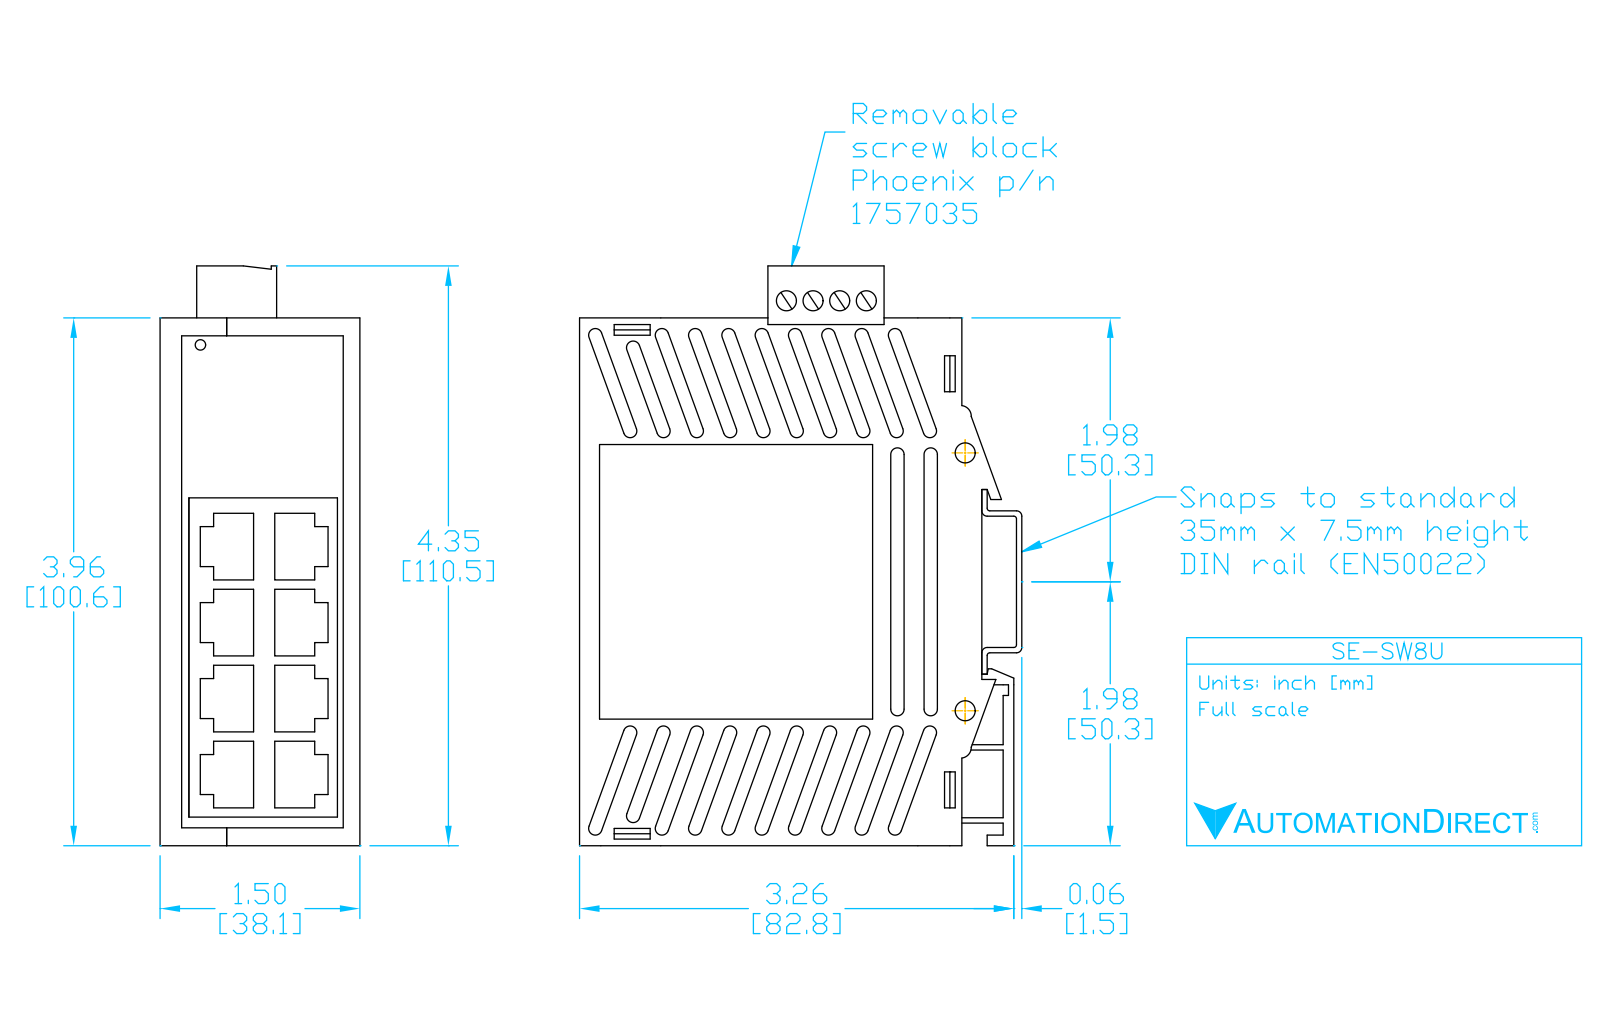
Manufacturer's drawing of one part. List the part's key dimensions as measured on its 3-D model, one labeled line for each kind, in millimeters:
Part name (STEP PRODUCT): SE-SW8U
STEP written by: SolidWorks 2011 (AUTOMOTIVE_DESIGN)
Units: millimetres
Bodies: 24 solids, 1055 faces (741 planar, 261 cylindrical, 53 other)
Overall size (bounding box): 109.51 × 83.06 × 38.09
Volume: 46 053 mm³ · Surface area: 76 051 mm²
Round holes (diameter × count): ⌀3.81 ×6, ⌀2.05 ×1
Round bosses / shafts (diameter × count): ⌀5.81 ×1, ⌀3.81 ×1
Partial cylindrical surfaces — rounded edges, fillets, slot ends (radius × count): R1.27 ×44, R2.27 ×44, R1.02 ×1, R1.05 ×1, R1.11 ×1, R2.02 ×1, R2.03 ×1, R2.05 ×1
Main face-to-face distances: 1, 36.84, 1.25, 36.59, 37.84, 35.59, 37.59, 99.58, 38.09, 37.09
Hole centre spacings: 5.08, 5.17, 7.01, 10.16, 10.21, 15.27, 33.76, 37.58
